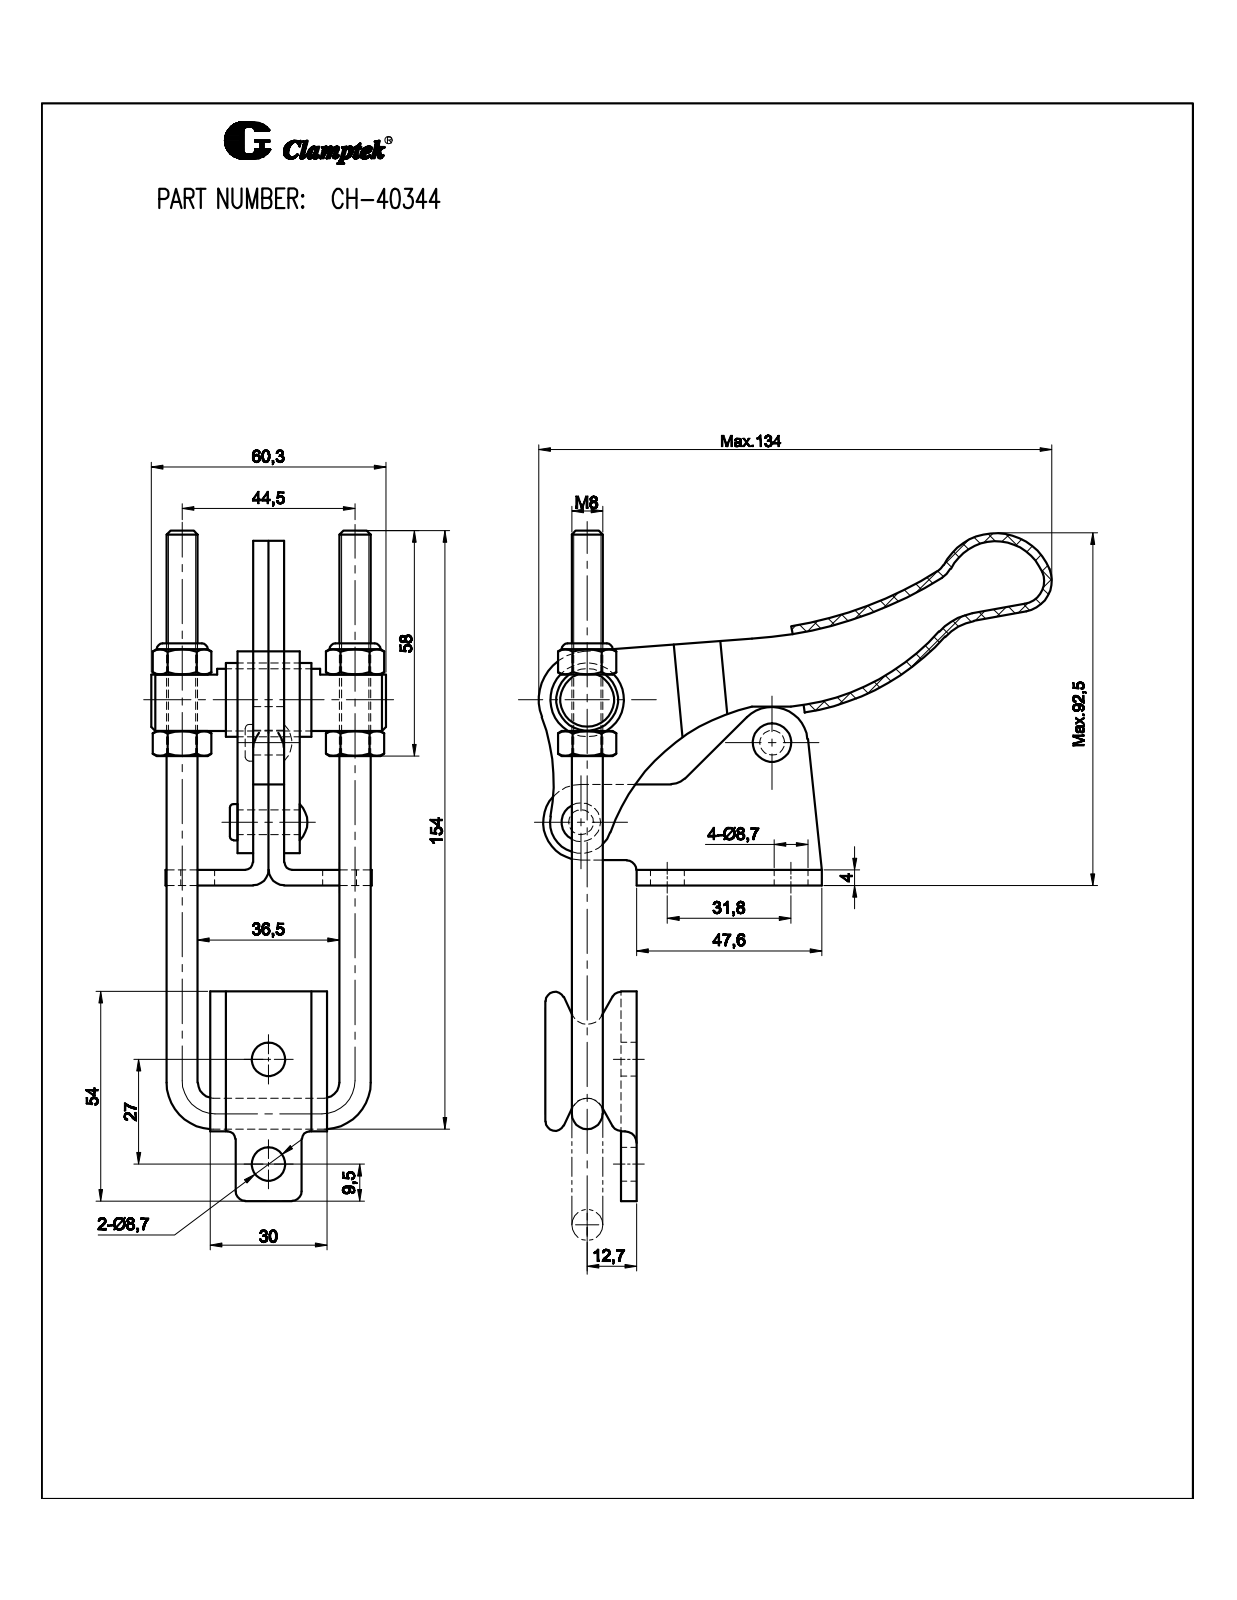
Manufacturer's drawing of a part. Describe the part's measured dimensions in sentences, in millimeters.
The part is named "CH-40344; M8防松_默认". Its 3-D file was written by "SolidWorks 2008 (CONFIG_CONTROL_DESIGN)". It is 15 solids with 1414 faces: 627 planar, 544 cylindrical and 243 other. Overall it measures 196.25 by 131.13 by 60.3 millimeters. Its volume is 94 091 cubic millimeters and its surface area 60 926 square millimeters. Round holes: 4 of diameter 8.7, 3 of diameter 6.5, 2 of diameter 8.4, 2 of diameter 8.5, 1 of diameter 1.19, 1 of diameter 4.39, 1 of diameter 6, 1 of diameter 6.4, 1 of diameter 8, 1 of diameter 15.8, 1 of diameter 19. Round bosses or shafts: 3 of diameter 8, 2 of diameter 11, 1 of diameter 1.05. Partial cylindrical surfaces (rounded edges, fillets, slot ends): 12 of radius 4, 5 of radius 2.5, 4 of radius 1.5, 4 of radius 2, 3 of radius 5, 2 of radius 4.25, 2 of radius 6, 2 of radius 13. The main face-to-face distances are 4, 8, 1.5, 12, 5.5, 9.5, 13.5, 2.5, 26, 7.1. The hole center spacings are 44.5, 31.8, 36.5, 48.41, 27, 27.22, 31.54, 33.32.
